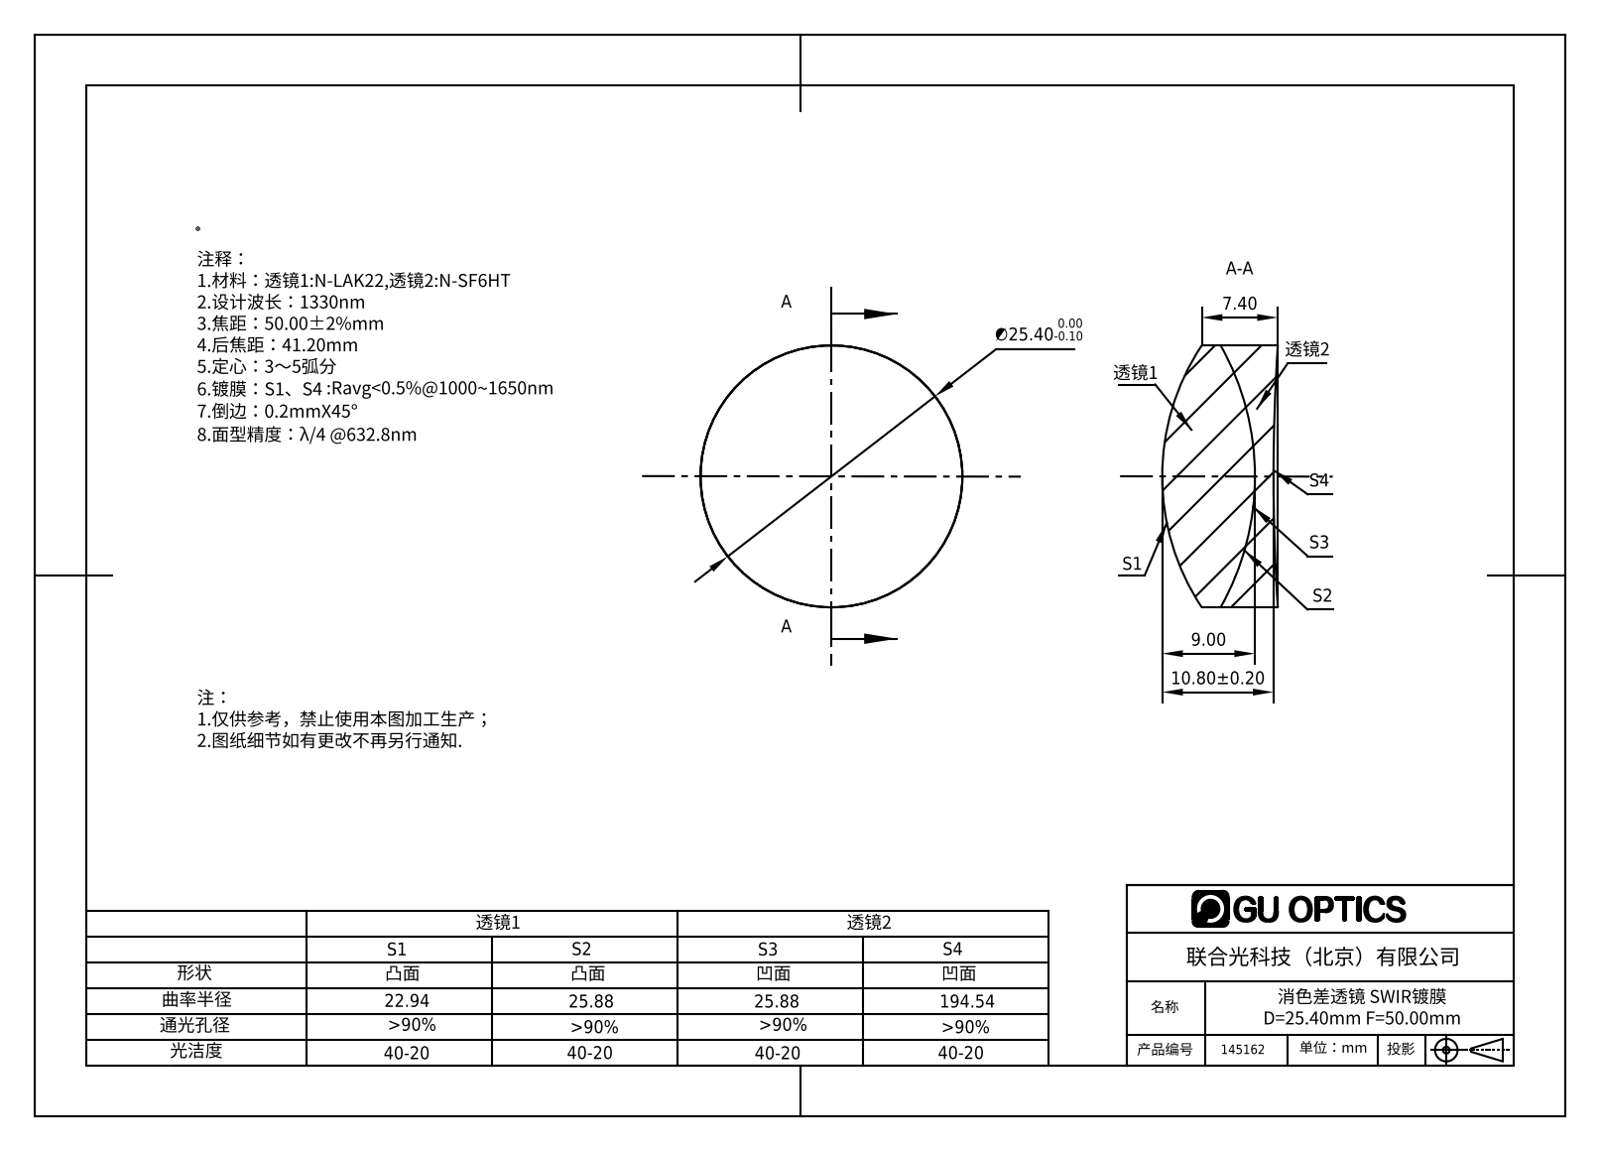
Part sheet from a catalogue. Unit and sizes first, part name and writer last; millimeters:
Units: millimetres
Overall size (bounding box): 25.4 × 25.4 × 11.21
Round bosses / shafts (diameter × count): ⌀25.4 ×1
Volume: 4 635 mm³ · Surface area: 2 732 mm²
Bodies: 2 solids, 12 faces (0 planar, 4 cylindrical, 8 other)
Part name (STEP PRODUCT): 145162
STEP written by: SolidWorks 2016 (AUTOMOTIVE_DESIGN)
